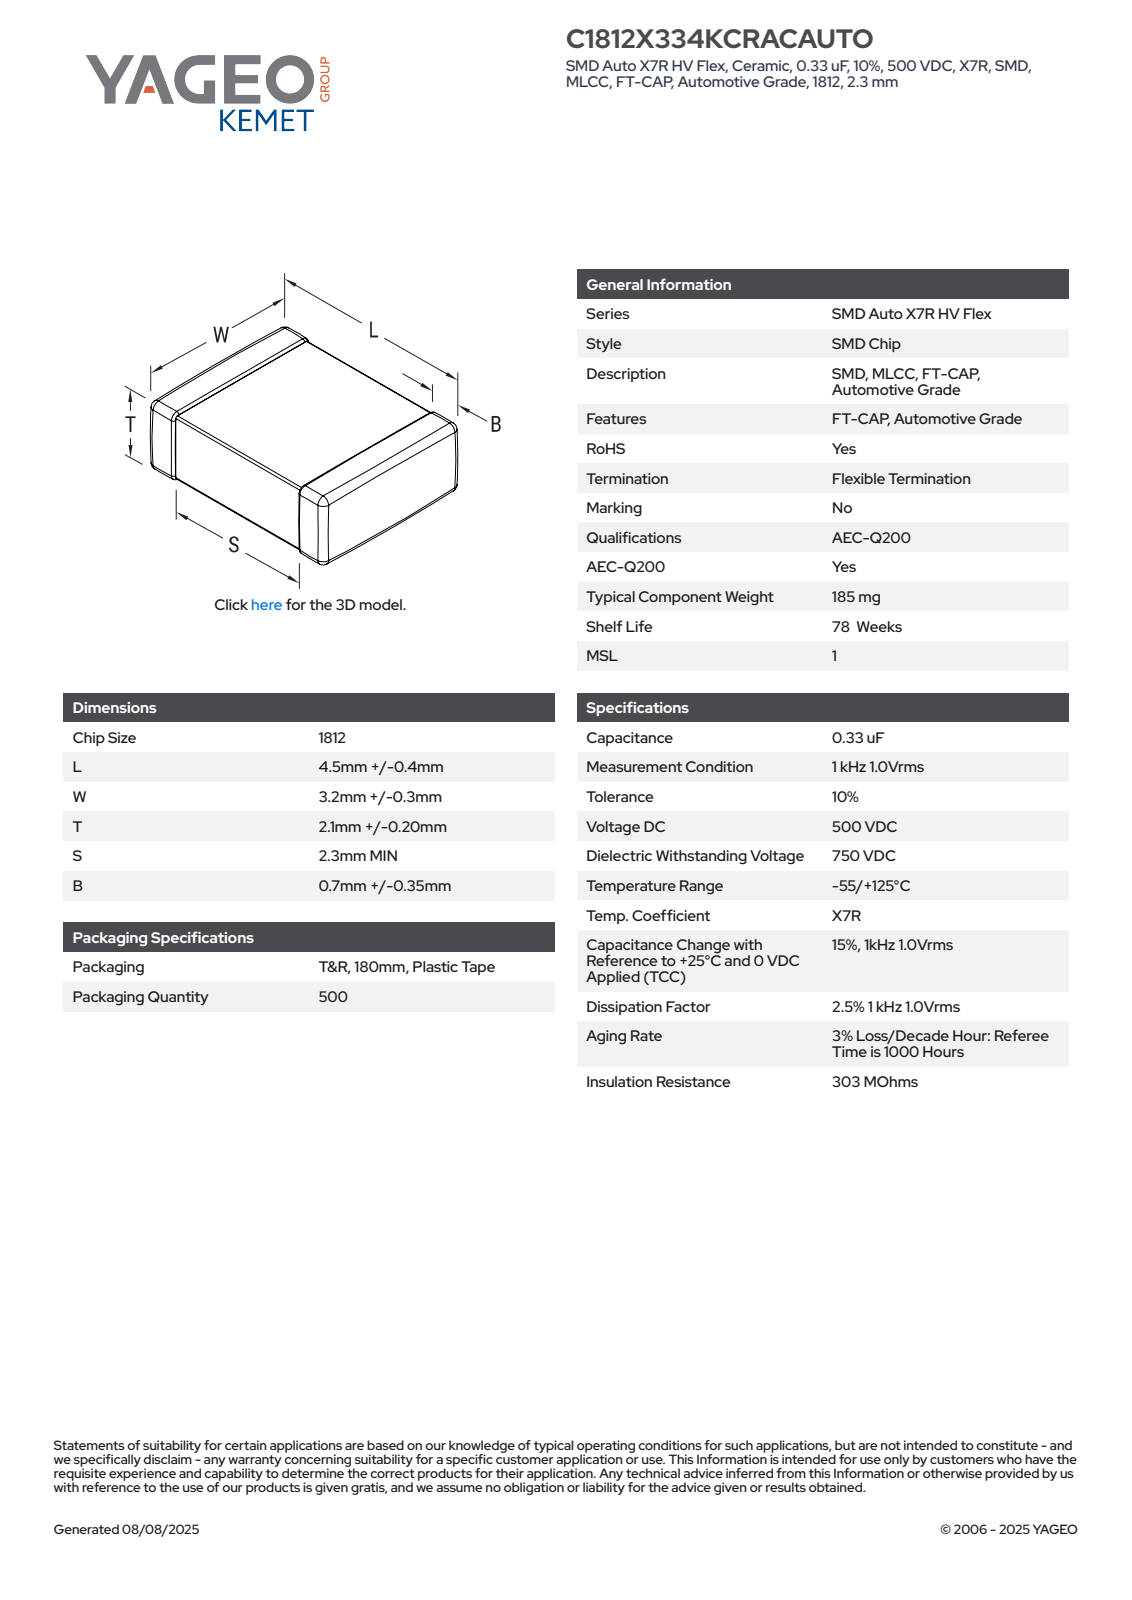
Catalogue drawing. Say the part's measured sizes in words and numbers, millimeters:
The part is named "CCS_CCSTD_1812_L4.9W3.5T2.3B0.7". Its 3-D file was written by "SolidWorks 2021 (AUTOMOTIVE_DESIGN)". It is 4 solids with 121 faces: 71 planar, 34 cylindrical and 16 other. Overall it measures 4.9 by 3.5 by 2.3 millimeters. Its volume is 37 cubic millimeters and its surface area 73 square millimeters. The main face-to-face distances are 2.23, 2.16, 3.43, 4.9, 2.3, 3.36, 3.5, 0.52, 2.25, 2.13.
